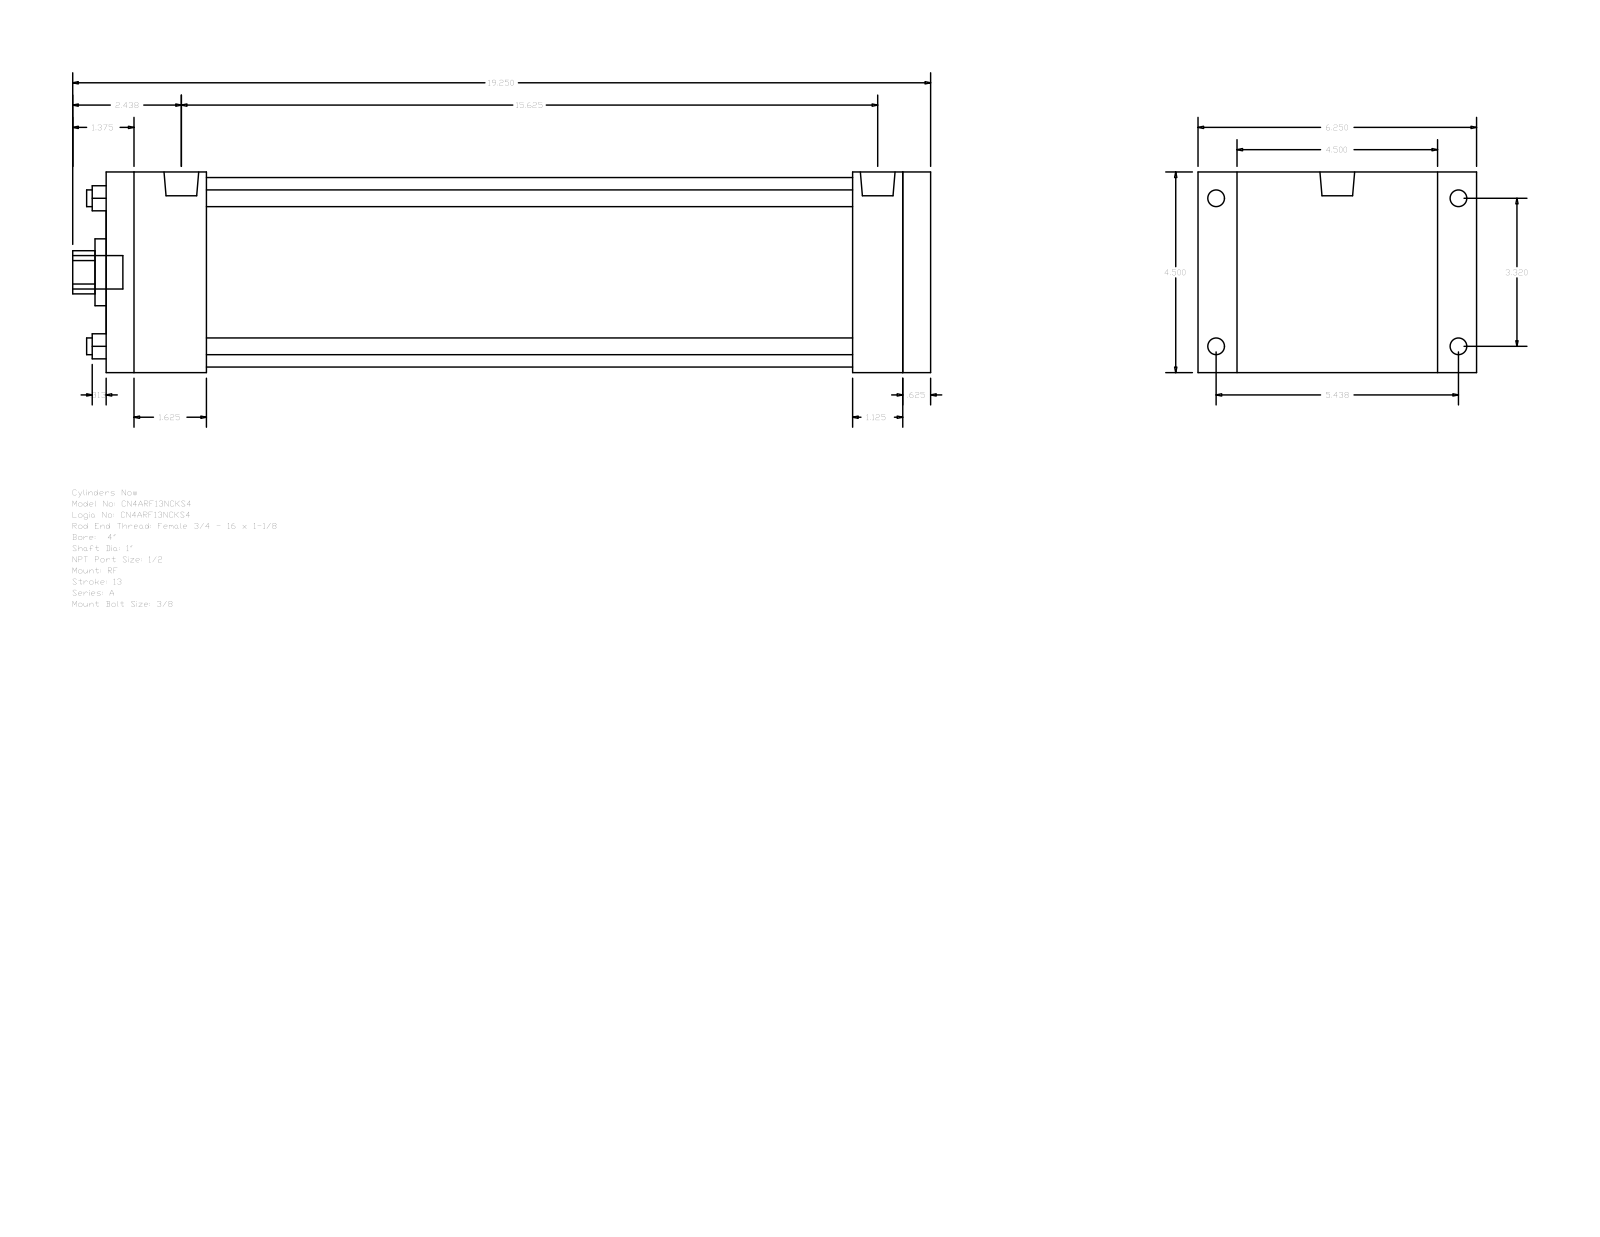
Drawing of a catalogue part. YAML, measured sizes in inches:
part_name: "A_RF__0400_1"
step_written_by: "GSSL Pune (CONFIG_CONTROL_DESIGN)"
units: inches
bodies: {solids: 0, faces: 92, planar: 64, cylindrical: 28, other: 0}
overall_size: [19.25, 6.25, 4.5]
round_holes:
  - {diameter: 0.375, count: 4}
  - {diameter: 1, count: 1}
  - {diameter: 1.5, count: 1}
  - {diameter: 4.25, count: 1}
round_bosses_or_shafts:
  - {diameter: 0.375, count: 4}
  - {diameter: 0.344, count: 4}
  - {diameter: 0.778, count: 2}
  - {diameter: 0.75, count: 1}
partial_cylinders:
  - {radius: 0.484, count: 1}
face_to_face_distances: [4.5, 18.5, 17.875, 0.625, 1.125, 0.875, 5.375, 16.75, 1.75, 2.25]
hole_center_spacings: [2.347, 3.32, 4.695]
